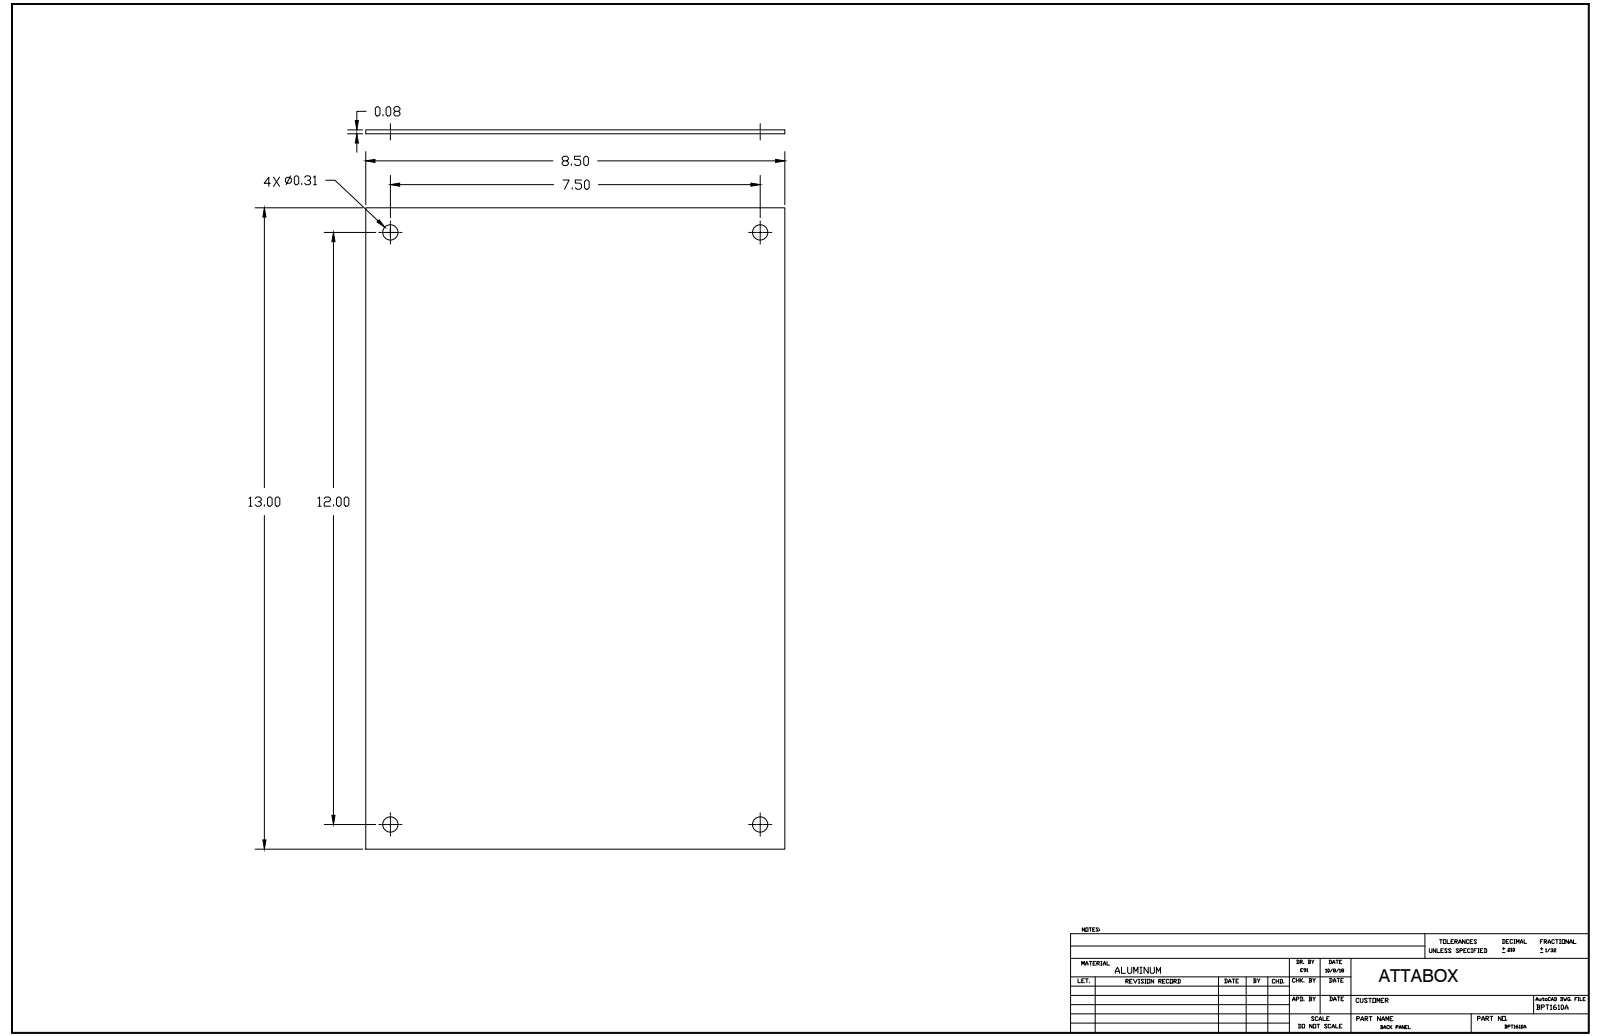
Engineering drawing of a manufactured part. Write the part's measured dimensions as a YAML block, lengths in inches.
part_name: "BP1610AL_STP"
step_written_by: "Autodesk Inventor 2014 (AUTOMOTIVE_DESIGN)"
units: inches
bodies: {solids: 1, faces: 10, planar: 6, cylindrical: 4, other: 0}
overall_size: [13, 8.5, 0.09]
volume: 9.918
surface_area: 224.6
round_holes:
  - {diameter: 0.31, count: 4}
face_to_face_distances: [0.09, 8.5, 13]
hole_center_spacings: [7.5, 12, 14.151]
